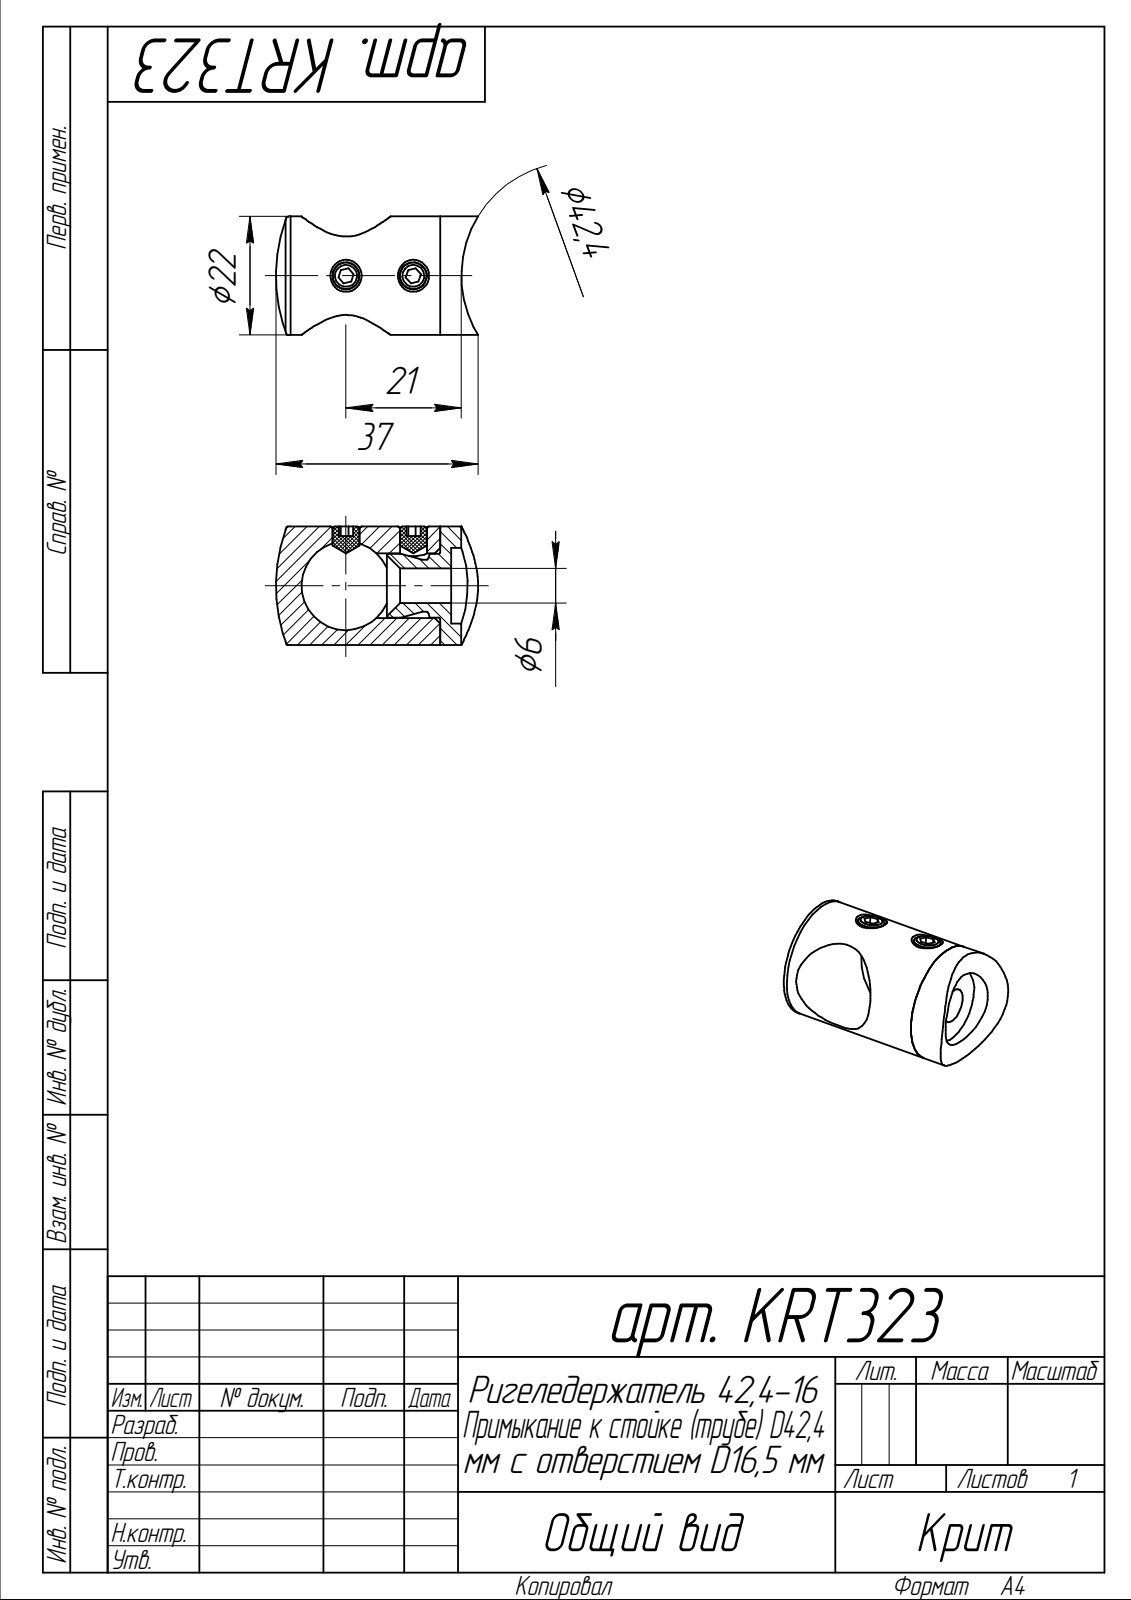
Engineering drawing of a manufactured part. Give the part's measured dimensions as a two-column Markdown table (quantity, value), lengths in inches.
| quantity | value |
| --- | --- |
| part name | socket set screw cone point_am_B18.3.6M - M5 x 0.8 x 5 Hex Socket Cone Pt. SS --N; арт. KRT323.001; арт. KRT323; арт. KRT323.002 |
| STEP written by | SolidWorks 2014 (AUTOMOTIVE_DESIGN) |
| units | inches |
| bodies | 4 solids, 78 faces (21 planar, 27 cylindrical, 30 other) |
| overall size | 1.476 × 0.866 × 0.866 |
| volume | 0.468 in³ |
| surface area | 8.373 in² |
| round holes (diameter × count) | 0.197 × 2, 0.252 × 1, 0.472 × 1, 0.551 × 1, 0.65 × 1 |
| round bosses / shafts (diameter × count) | 0.866 × 1, 0.465 × 1, 0.382 × 1 |
| partial cylindrical surfaces (radius × count) | 0.835 × 1 |
| main face-to-face distances | 0.079, 0.098, 0.067, 0.467, 0.099, 0.368, 0.565, 0.369, 0.198, 0.466 |
| hole center spacings | 0.492 |
